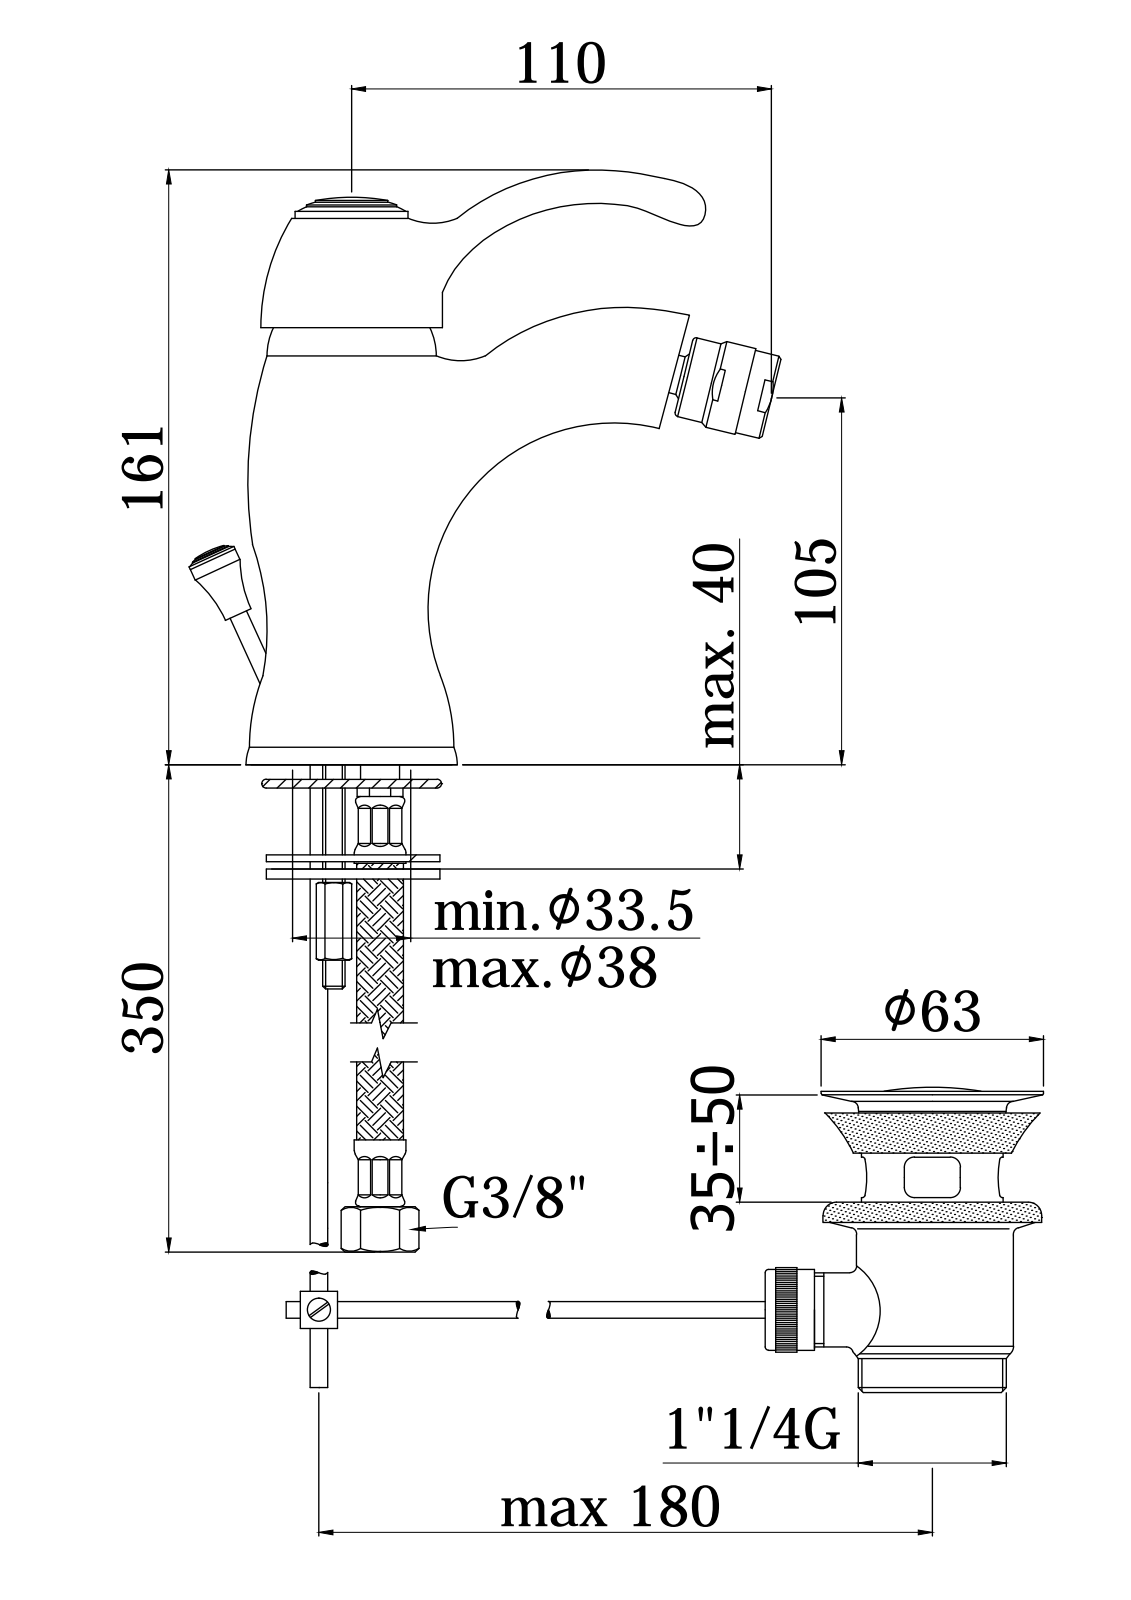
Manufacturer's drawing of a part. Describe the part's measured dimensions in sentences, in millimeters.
The part is named "FA135CR". Its 3-D file was written by "CREO PARAMETRIC BY PTC INC, 2020044 (CONFIG_CONTROL_DESIGN)". It is 5 solids with 2944 faces: 2046 planar, 429 cylindrical and 469 other. Overall it measures 176.7 by 164.93 by 62 millimeters. Its volume is 229 495 cubic millimeters and its surface area 124 909 square millimeters. Round holes: 5 of diameter 8, 4 of diameter 5, 3 of diameter 7, 3 of diameter 11, 2 of diameter 3.3, 2 of diameter 4, 2 of diameter 4.6, 2 of diameter 9, 2 of diameter 12, 2 of diameter 21, 1 of diameter 5.5, 1 of diameter 15. Round bosses or shafts: 2 of diameter 25.8, 2 of diameter 15.9, 2 of diameter 10.8, 2 of diameter 9.4, 2 of diameter 8.5, 2 of diameter 8.2, 2 of diameter 6, 1 of diameter 50.9. Partial cylindrical surfaces (rounded edges, fillets, slot ends): 53 of radius 0.5, 24 of radius 0.2, 19 of radius 1, 8 of radius 1.5, 4 of radius 0.3, 4 of radius 5.5, 2 of radius 7.5, 2 of radius 8.25. The main face-to-face distances are 2.5, 5.5, 6, 63, 1, 5, 144.4, 7.5, 57.5, 138.9. The hole center spacings are 13.6, 0.5, 2, 2.06, 7.92, 8.36, 8.6, 8.79.
